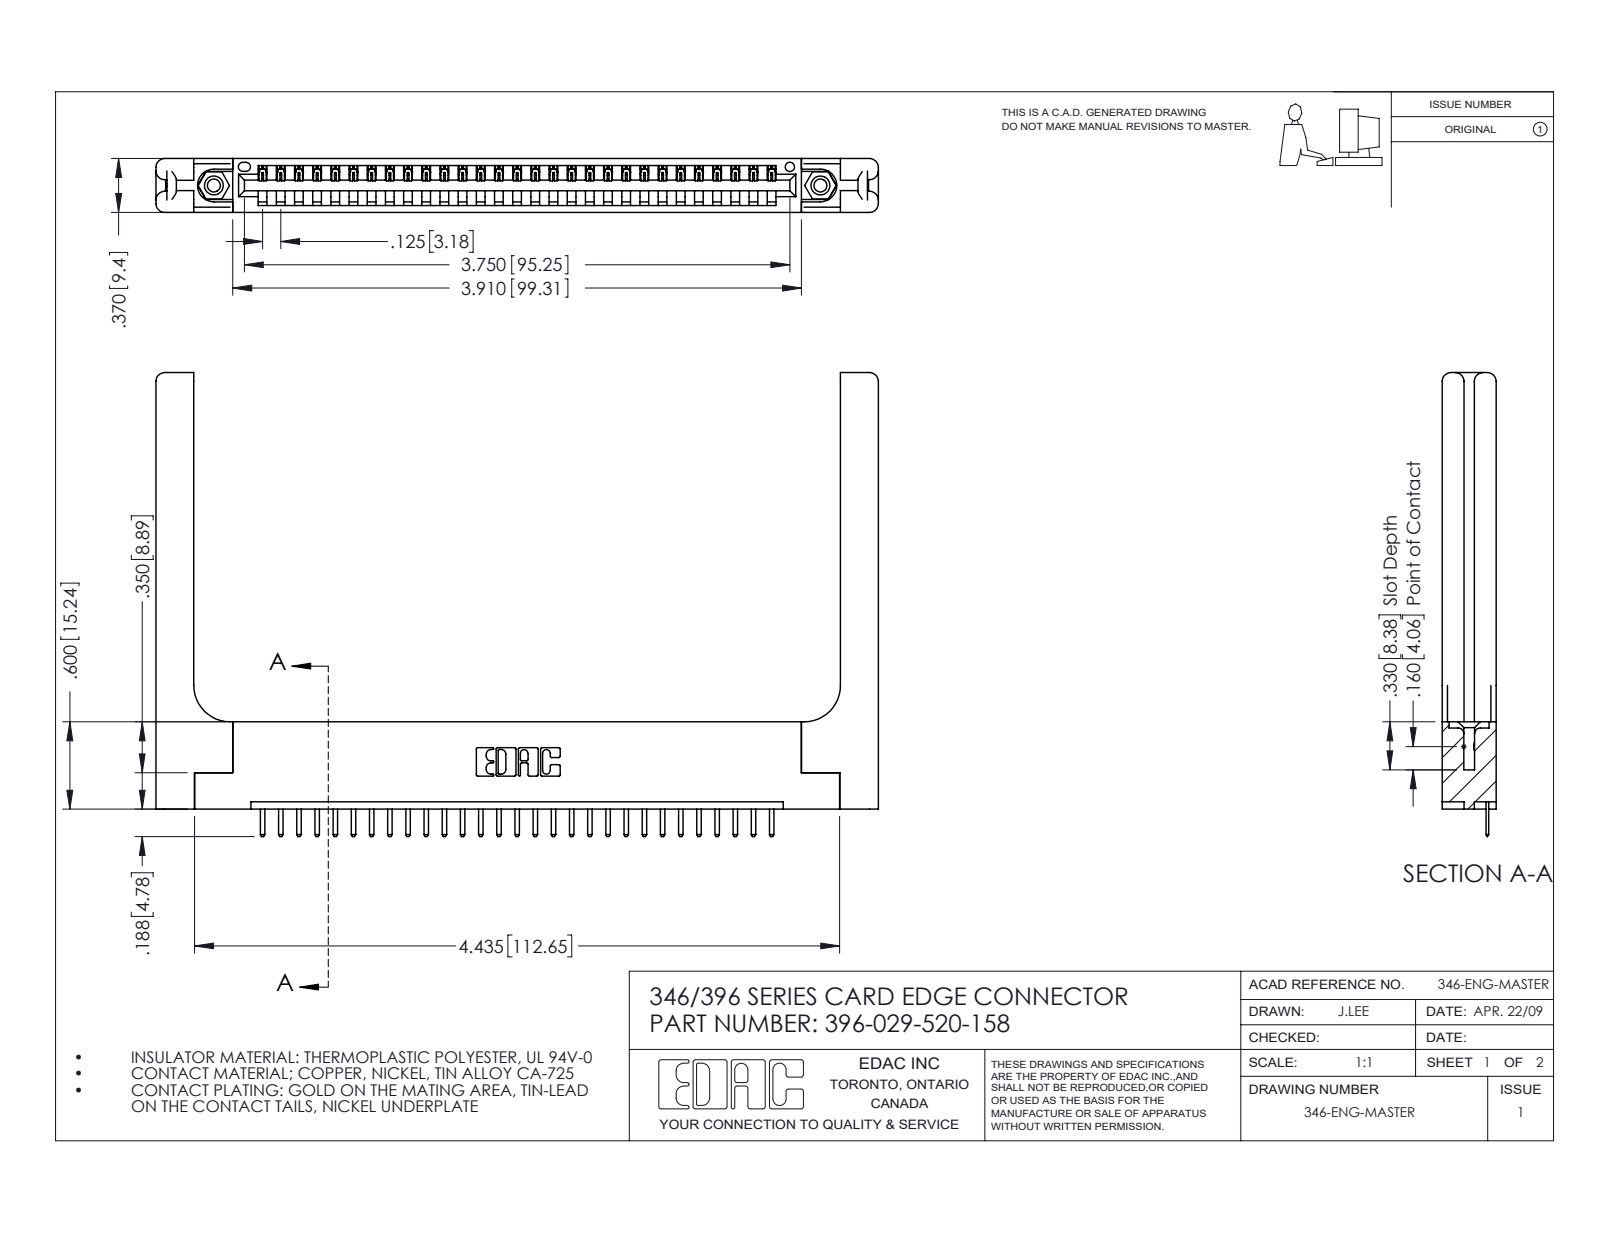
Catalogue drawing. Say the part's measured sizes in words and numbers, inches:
The part is named "396-029-520-158; 346-220-058_345-220-058; 346 Part_Flush Mounting Lugs - 0.156 Dia-TH; 345-250-001_345-250-001-102 (+1 more)". Its 3-D file was written by "SolidWorks 2016 (CONFIG_CONTROL_DESIGN)". It is 34 solids with 2176 faces: 1442 planar, 674 cylindrical and 60 other. Overall it measures 4.966 by 3.188 by 0.37 inches. Its volume is 1.185 cubic inches and its surface area 30.42 square inches. Round holes: 2 of diameter 0.089, 2 of diameter 0.125, 2 of diameter 0.156, 1 of diameter 0.064. Round bosses or shafts: 2 of diameter 0.155. Partial cylindrical surfaces (rounded edges, fillets, slot ends): 60 of radius 0.01, 58 of radius 0.006, 22 of radius 0.01, 16 of radius 0.06, 6 of radius 0.007, 6 of radius 0.031, 3 of radius 0.026, 2 of radius 0.03. The main face-to-face distances are 0.37, 0.072, 0.048, 0.322, 0.148, 0.15, 0.25, 0.298, 0.025, 0.076. The hole center spacings are 0.246, 3.962, 4.17.
